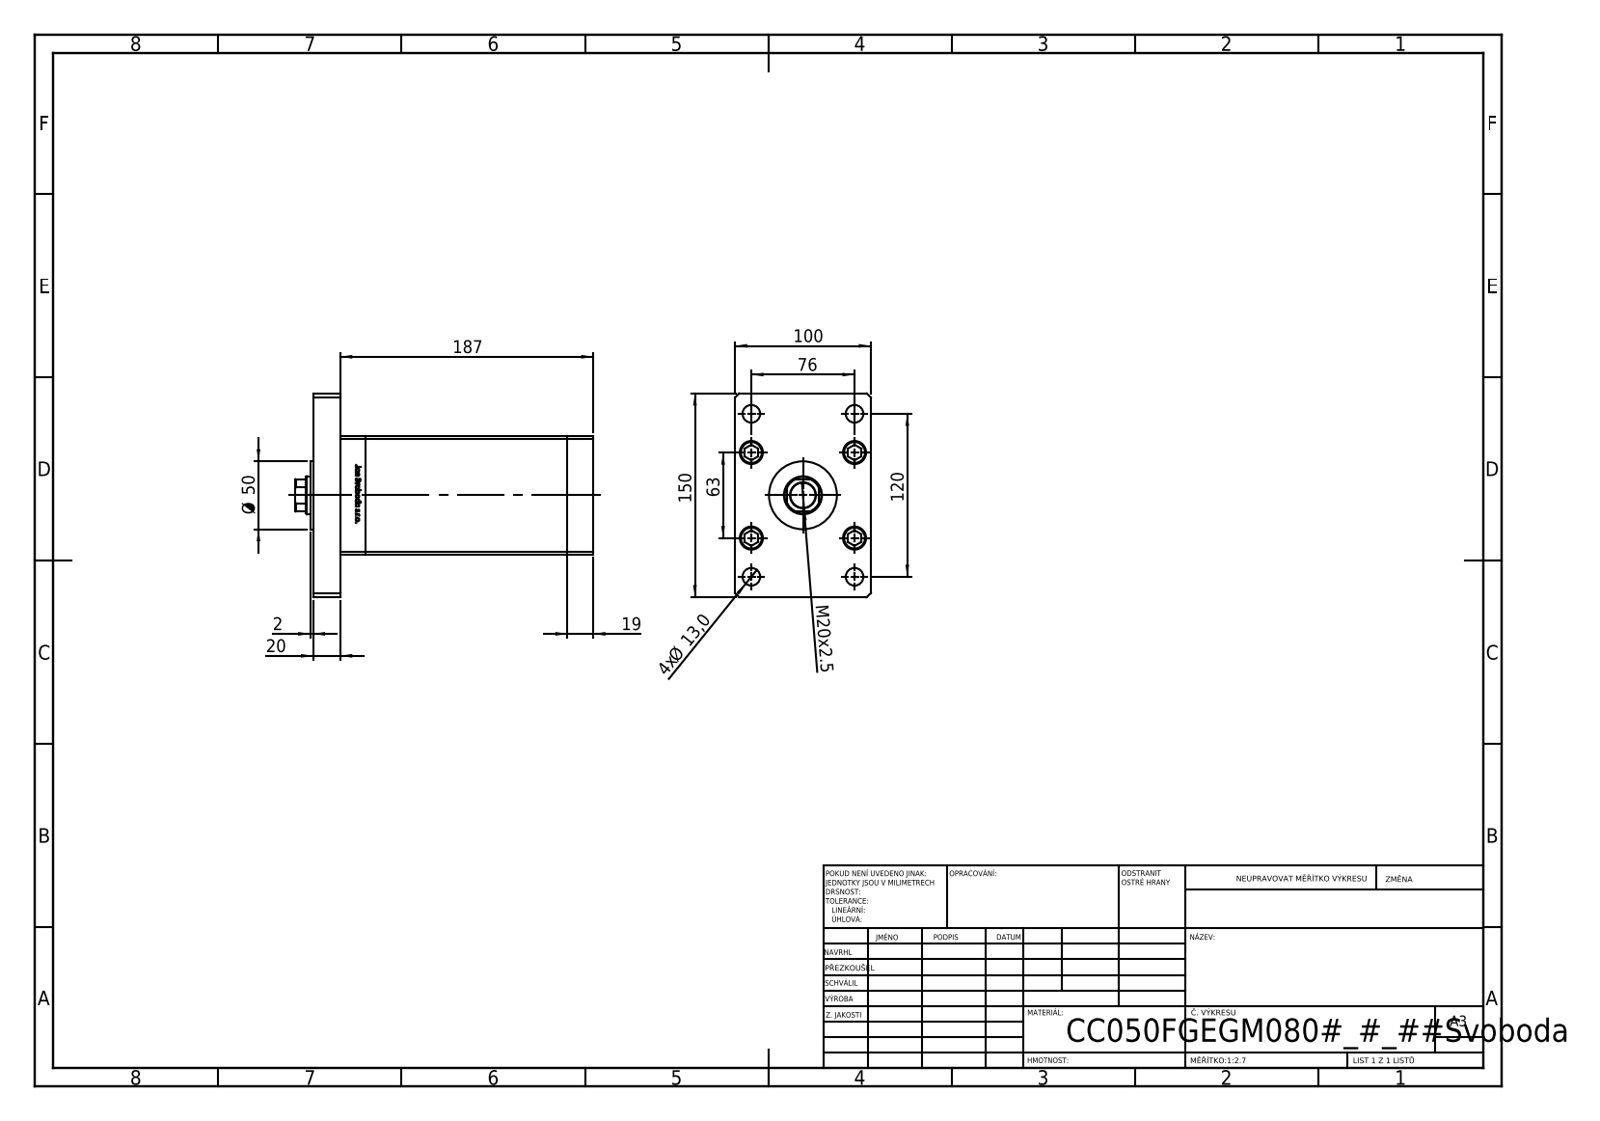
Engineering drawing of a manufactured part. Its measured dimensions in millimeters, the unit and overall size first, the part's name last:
Units: millimetres
Overall size (bounding box): 219.5 × 150 × 100
Round holes (diameter × count): ⌀13.5 ×7, ⌀18 ×7, ⌀12 ×4, ⌀13 ×4, ⌀17 ×4, ⌀2 ×2, ⌀13.16 ×2, ⌀18.5 ×1, ⌀28 ×1, ⌀29.5 ×1
Round bosses / shafts (diameter × count): ⌀8 ×9, ⌀17 ×5, ⌀50 ×1
Partial cylindrical surfaces — rounded edges, fillets, slot ends (radius × count): R0.93 ×2, R13.5 ×1
Main face-to-face distances: 19, 167.5, 100, 87, 20, 148.5, 39, 187.5, 186.5, 206.5
Hole centre spacings: 34, 18.59, 28.5, 37.13, 39.64, 49.36, 57.95, 71.02
Volume: 1 705 000 mm³ · Surface area: 259 381 mm²
Bodies: 19 solids, 1311 faces (517 planar, 188 cylindrical, 606 other)
Part name (STEP PRODUCT): ALLEN BOLT; V220C_F_MIDDLE; V220C_F; V220C BACK_F (+2 more)
STEP written by: SolidWorks 2019 (CONFIG_CONTROL_DESIGN)
